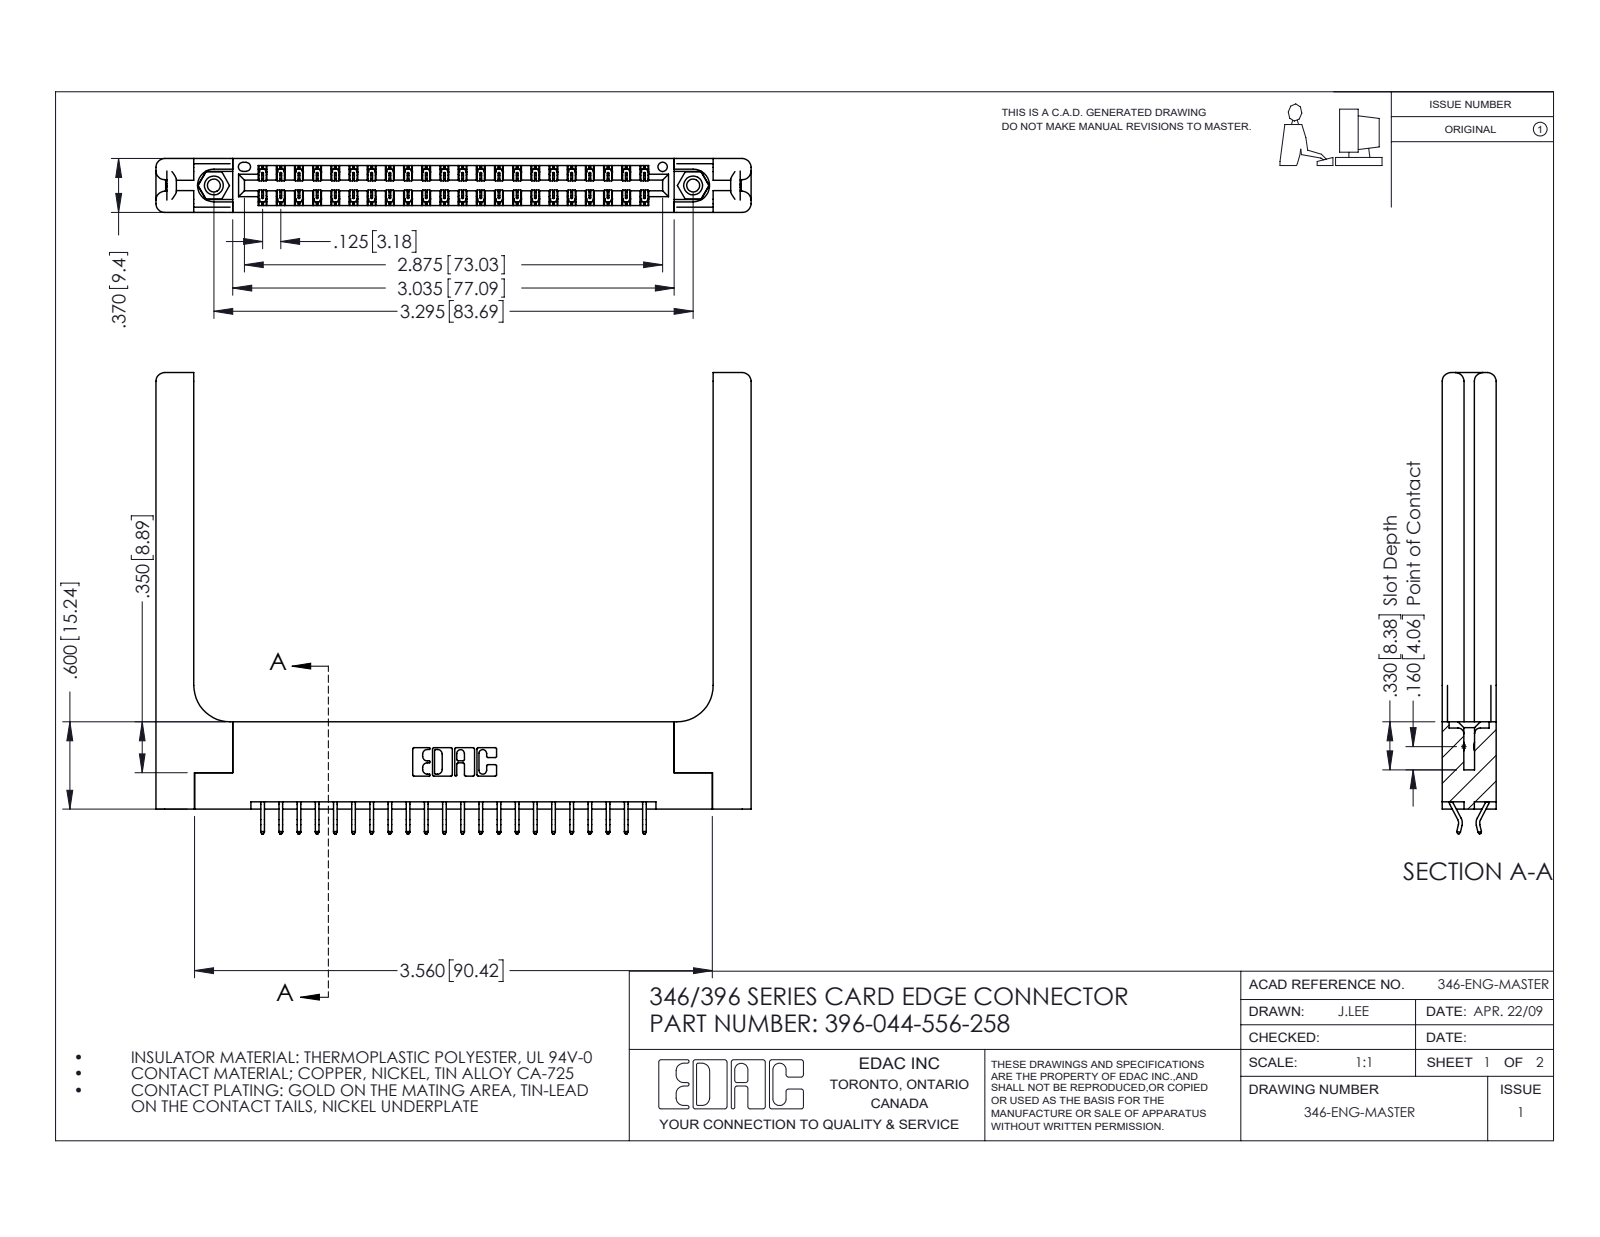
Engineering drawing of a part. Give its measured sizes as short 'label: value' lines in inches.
name: 346-220-058_345-220-058; 345-250-001_345-250-001-102; 396-044-556-258; 345-292-001_556 Tail (+1 more)
written by: SolidWorks 2016 (CONFIG_CONTROL_DESIGN)
unit: in
bodies: 49 solids, 2930 faces (1940 planar, 930 cylindrical, 60 other)
size: 4.091 × 3.17 × 0.37
volume: 1.066 in³; area: 28.41 in²
holes: 2× ⌀0.089, 2× ⌀0.125, 2× ⌀0.156, 1× ⌀0.064
bosses: 2× ⌀0.155
rounds: 66× R0.006, 22× R0.01, 16× R0.06, 6× R0.007, 6× R0.031, 3× R0.026, 2× R0.01, 2× R0.014
face distances: 0.37, 0.072, 0.048, 0.322, 0.148, 0.15, 0.25, 0.025, 0.298, 0.077
hole spacings: 0.246, 3.087, 3.295
